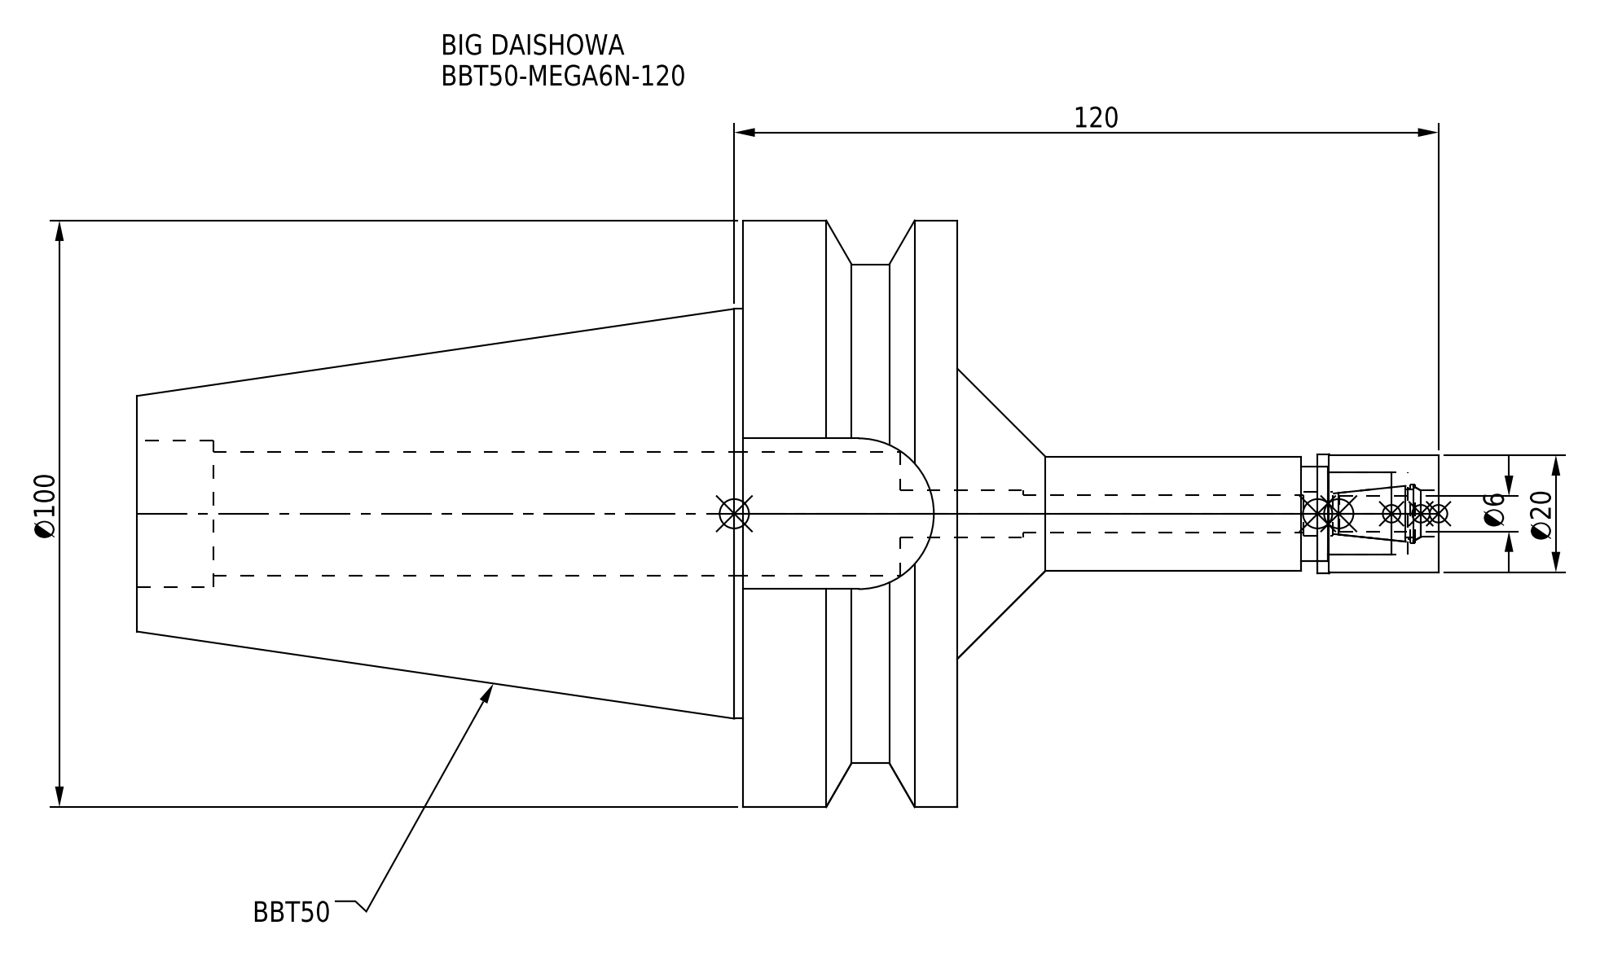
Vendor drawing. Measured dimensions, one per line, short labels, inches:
name: BBT50-MEGA6N-120_1.stp; DXF_TEMP_ASSY_ASM_4_ASM.stp; BBT50-MEGA6N-120-060.stp; MGN6_1.stp (+3 more)
written by: SolidWorks 2019 (CONFIG_CONTROL_DESIGN)
unit: in
bodies: 2 solids, 79 faces (23 planar, 42 cylindrical, 14 other)
size: 8.732 × 3.937 × 3.937
volume: 29.43 in³; area: 97.18 in²
holes: 1× ⌀0.252, 1× ⌀0.295, 1× ⌀0.311, 1× ⌀0.315, 1× ⌀0.335, 1× ⌀0.394, 1× ⌀0.551, 1× ⌀0.63, 1× ⌀0.835, 1× ⌀0.984
bosses: 1× ⌀3.937, 1× ⌀3.346, 1× ⌀2.75, 1× ⌀0.799, 1× ⌀0.787, 1× ⌀0.768
rounds: 1× R0.506
face distances: 1.437, 2.787, 5.504, 4.067, 1.012, 0.386, 1.051, 5.118, 3.228, 3.614
